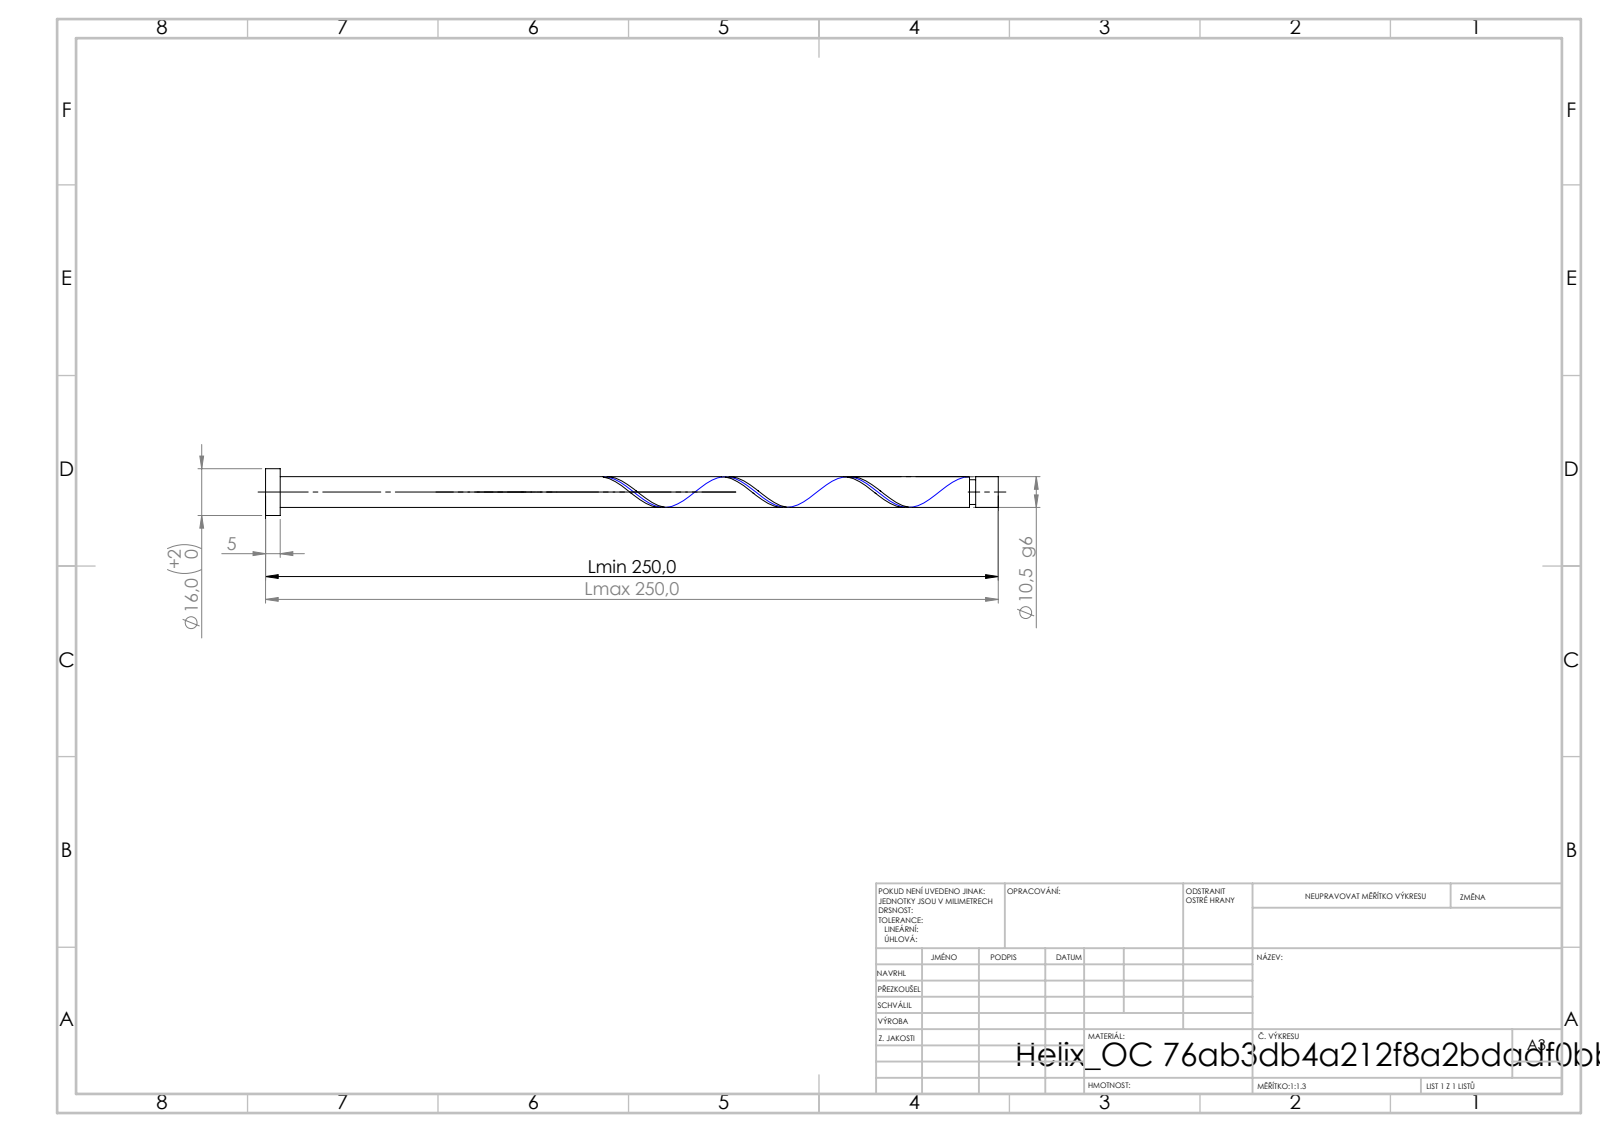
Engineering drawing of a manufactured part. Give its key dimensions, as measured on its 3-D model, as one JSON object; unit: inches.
{"step_written_by": "SolidWorks 2019 (CONFIG_CONTROL_DESIGN)", "units": "inches", "bodies": {"solids": 1, "faces": 21, "planar": 6, "cylindrical": 14, "other": 1}, "overall_size": [9.843, 0.63, 0.63], "volume_in3": 1.339, "surface_area_in2": 13.88, "round_bosses_or_shafts": [[0.63, 1], [0.413, 1], [0.331, 1]], "face_to_face_distances": [0.197, 9.843, 9.646, 9.609, 9.413, 0.233, 9.527, 9.33, 0.083, 0.316]}
